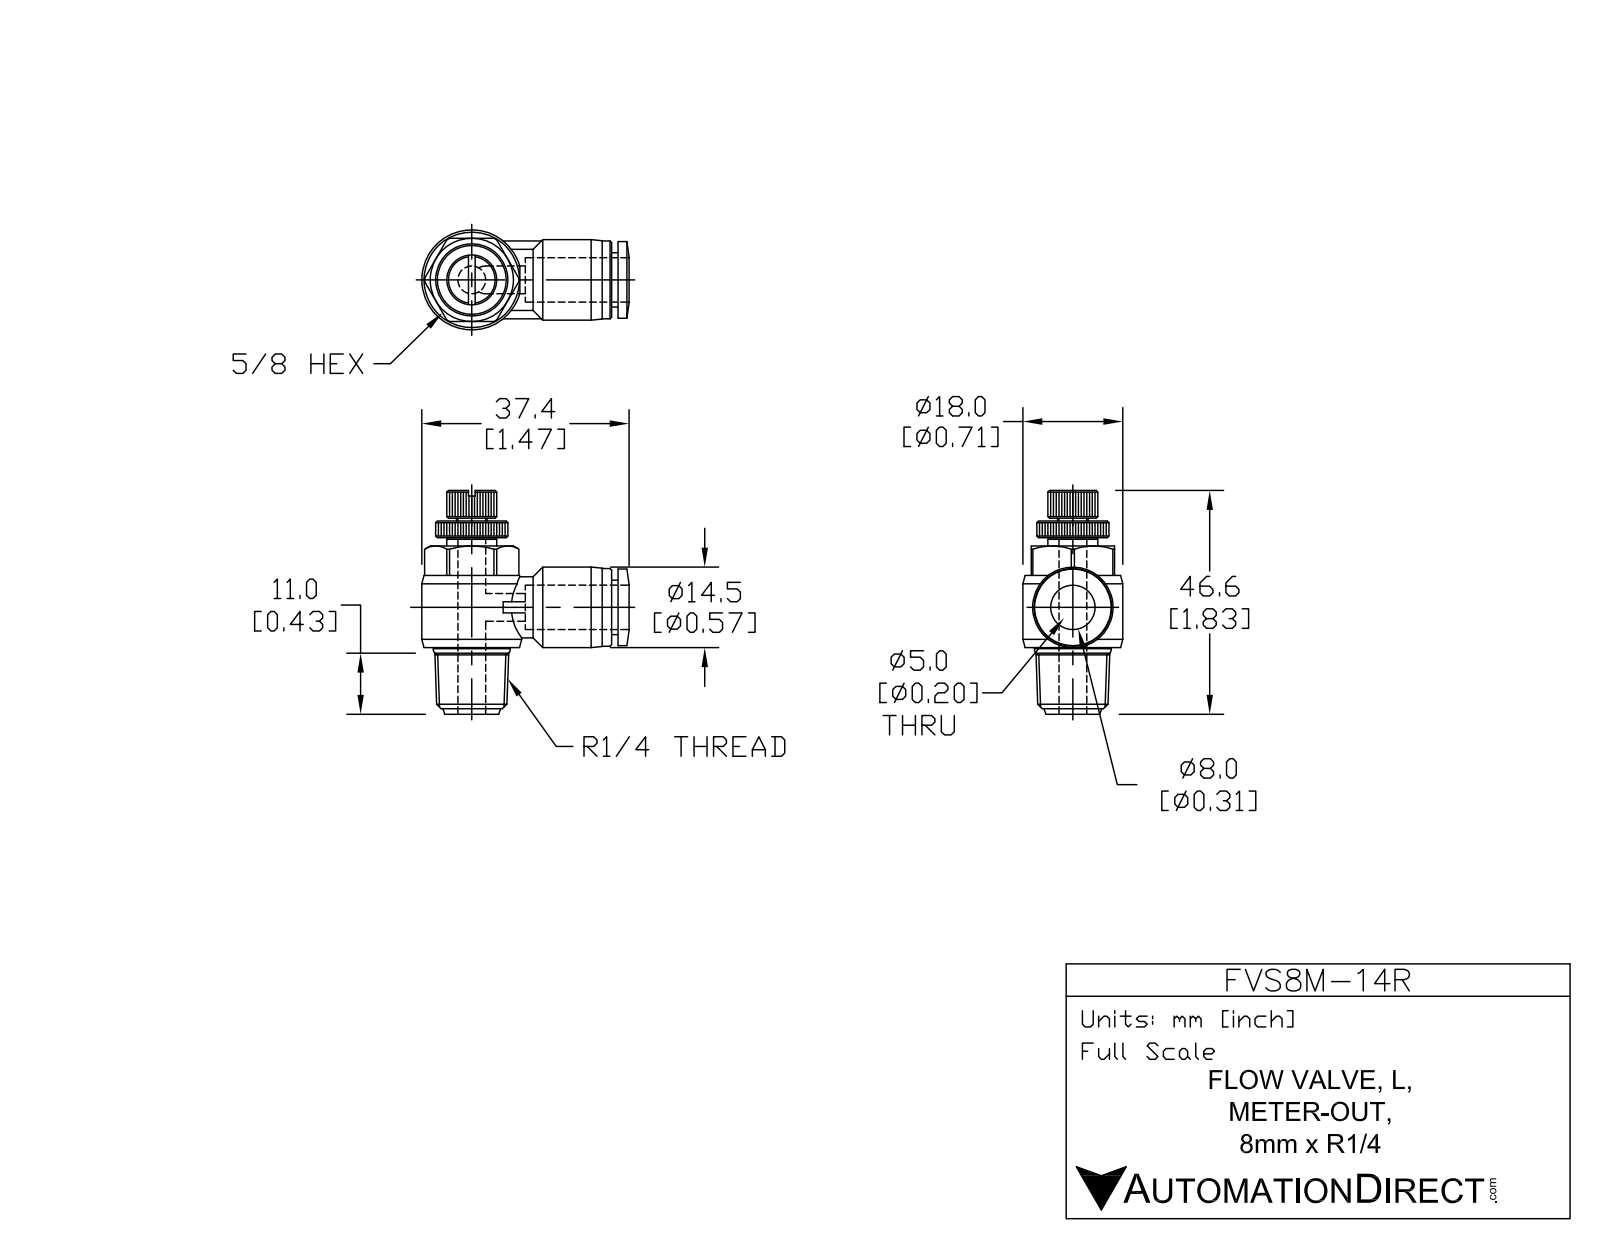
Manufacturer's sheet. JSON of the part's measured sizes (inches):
{"part_name": "FVS8M-14R", "step_written_by": "SolidWorks 2015 (AUTOMOTIVE_DESIGN)", "units": "inches", "bodies": {"solids": 1, "faces": 418, "planar": 187, "cylindrical": 111, "other": 120}, "overall_size": [1.835, 1.47, 0.709], "volume_in3": 0.495, "surface_area_in2": 7.06, "round_holes": [[0.177, 2], [0.327, 1]], "round_bosses_or_shafts": [[0.709, 1], [0.571, 1], [0.551, 1], [0.543, 1], [0.528, 1], [0.433, 1], [0.386, 1], [0.354, 1]], "partial_cylinders_radius": [[0.256, 1], [0.335, 1]], "face_to_face_distances": [0.591, 0.177, 0.701, 0.878, 1.173, 0.045, 0.76, 0.059, 0.118, 0.472]}
